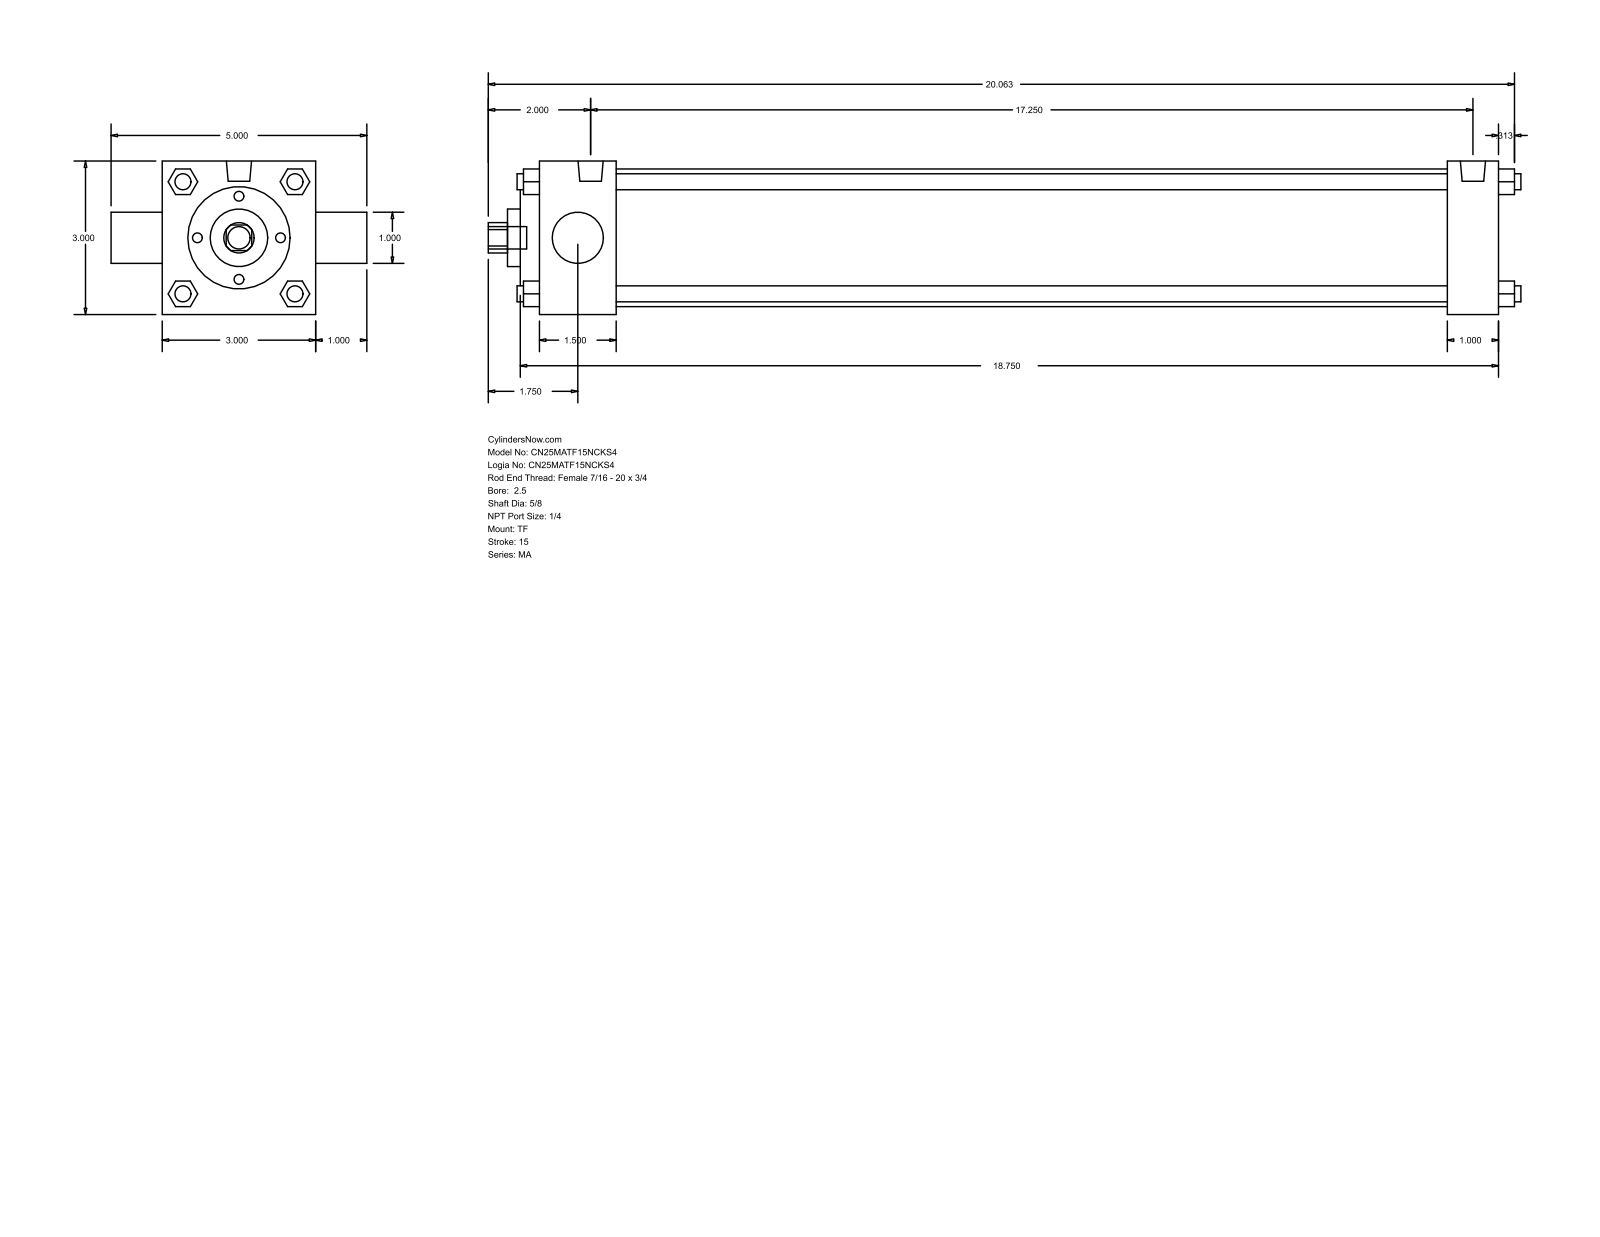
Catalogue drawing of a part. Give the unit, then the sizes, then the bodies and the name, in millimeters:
Units: millimetres
Overall size (bounding box): 512.76 × 127 × 76.2
Round holes (diameter × count): ⌀15.88 ×1, ⌀25.4 ×1, ⌀28.57 ×1, ⌀50.8 ×1, ⌀68.33 ×1
Round bosses / shafts (diameter × count): ⌀7.94 ×7, ⌀12.49 ×2, ⌀11.11 ×1
Partial cylindrical surfaces — rounded edges, fillets, slot ends (radius × count): R7.54 ×1
Main face-to-face distances: 76.2, 476.25, 25.4, 38.1, 450.85, 412.75, 438.15, 12.7, 9.52, 47.62
Bodies: 0 solids, 122 faces (93 planar, 29 cylindrical, 0 other)
Part name (STEP PRODUCT): MA_TF__0250_0.625
STEP written by: GSSL Pune (CONFIG_CONTROL_DESIGN)
